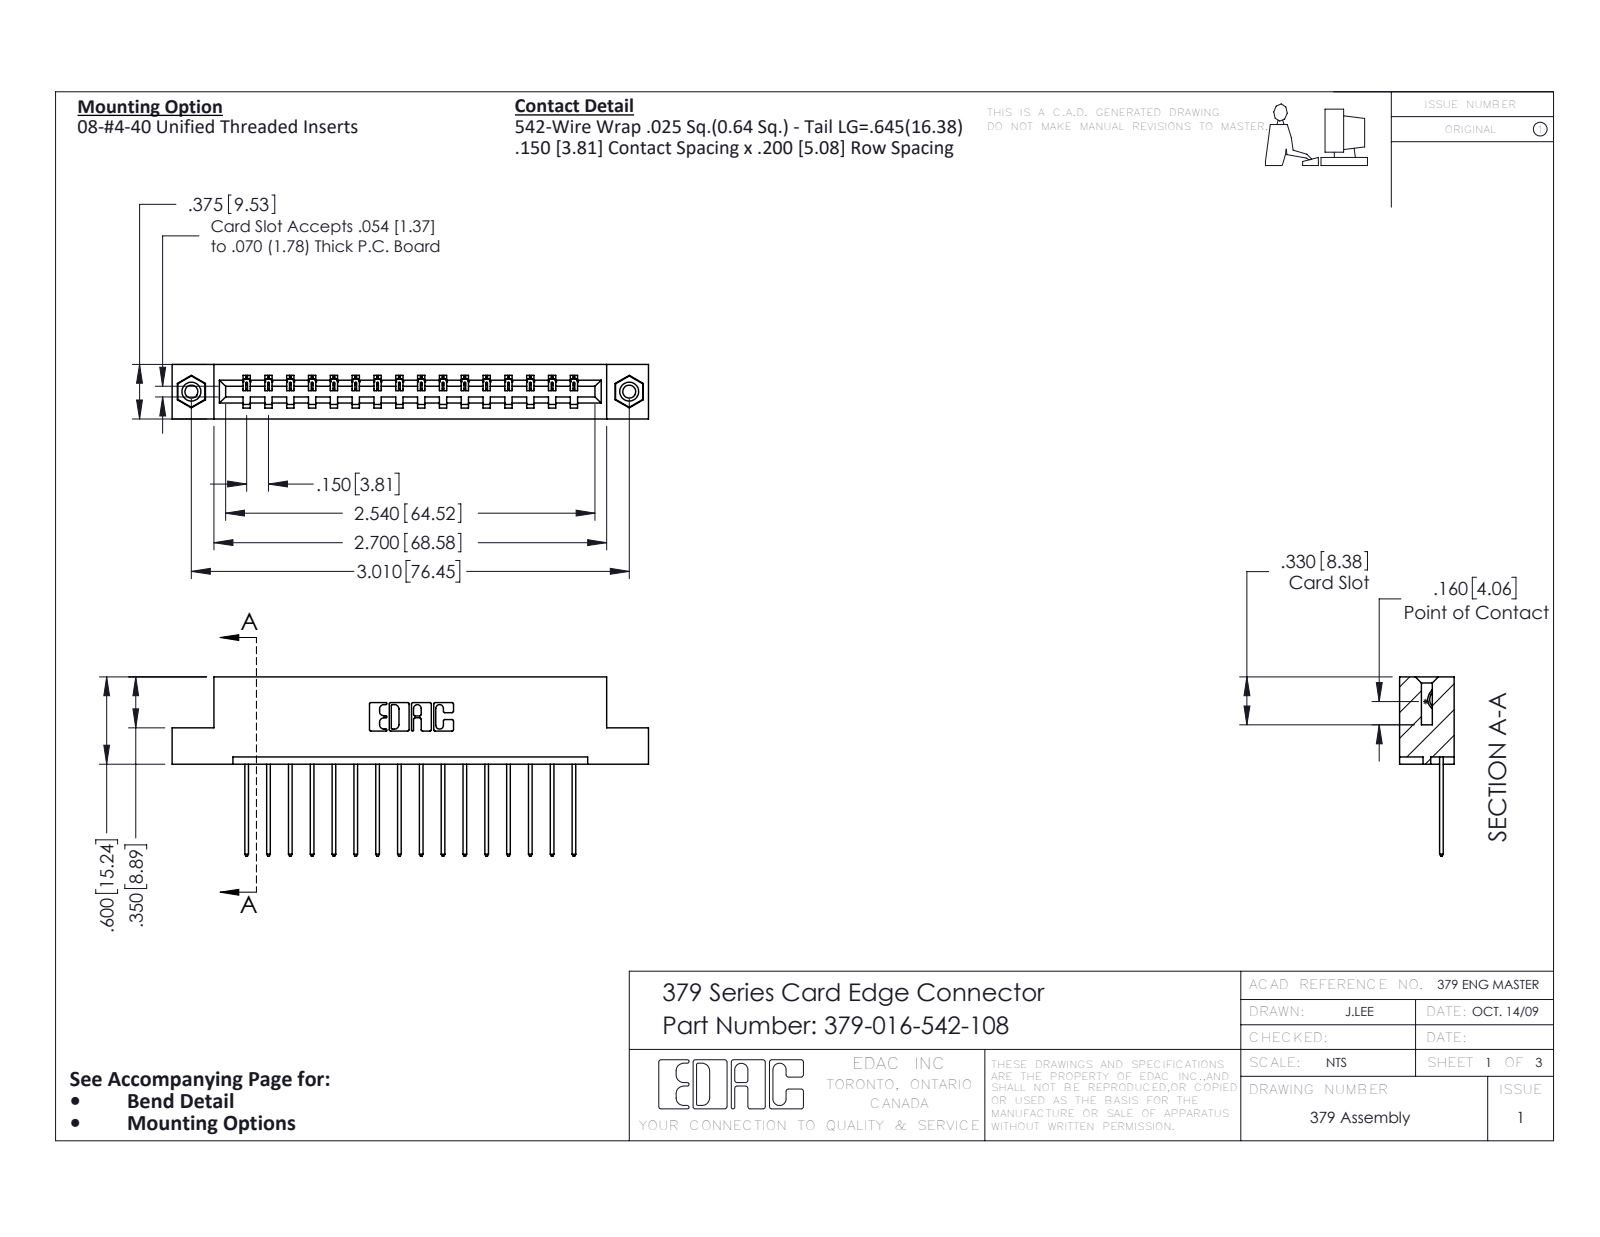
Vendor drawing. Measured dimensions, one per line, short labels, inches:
name: 345-292-001_345-293-142; 345-250-001_345-250-003-102; 379-016-542-108; 379 Part_Flush - .156 Dia - TI
written by: SolidWorks 2020 (CONFIG_CONTROL_DESIGN)
unit: in
bodies: 19 solids, 1102 faces (774 planar, 312 cylindrical, 16 other)
size: 3.275 × 1.232 × 0.375
volume: 0.516 in³; area: 13.62 in²
holes: 2× ⌀0.089, 2× ⌀0.125, 2× ⌀0.156
bosses: 2× ⌀0.155
rounds: 32× R0.006, 32× R0.01, 22× R0.01, 6× R0.007, 6× R0.031, 3× R0.026, 1× R0.014, 1× R0.022
face distances: 0.3, 0.075, 0.375, 0.6, 0.15, 0.225, 0.45, 0.2, 0.275, 0.1
hole spacings: 3.01
